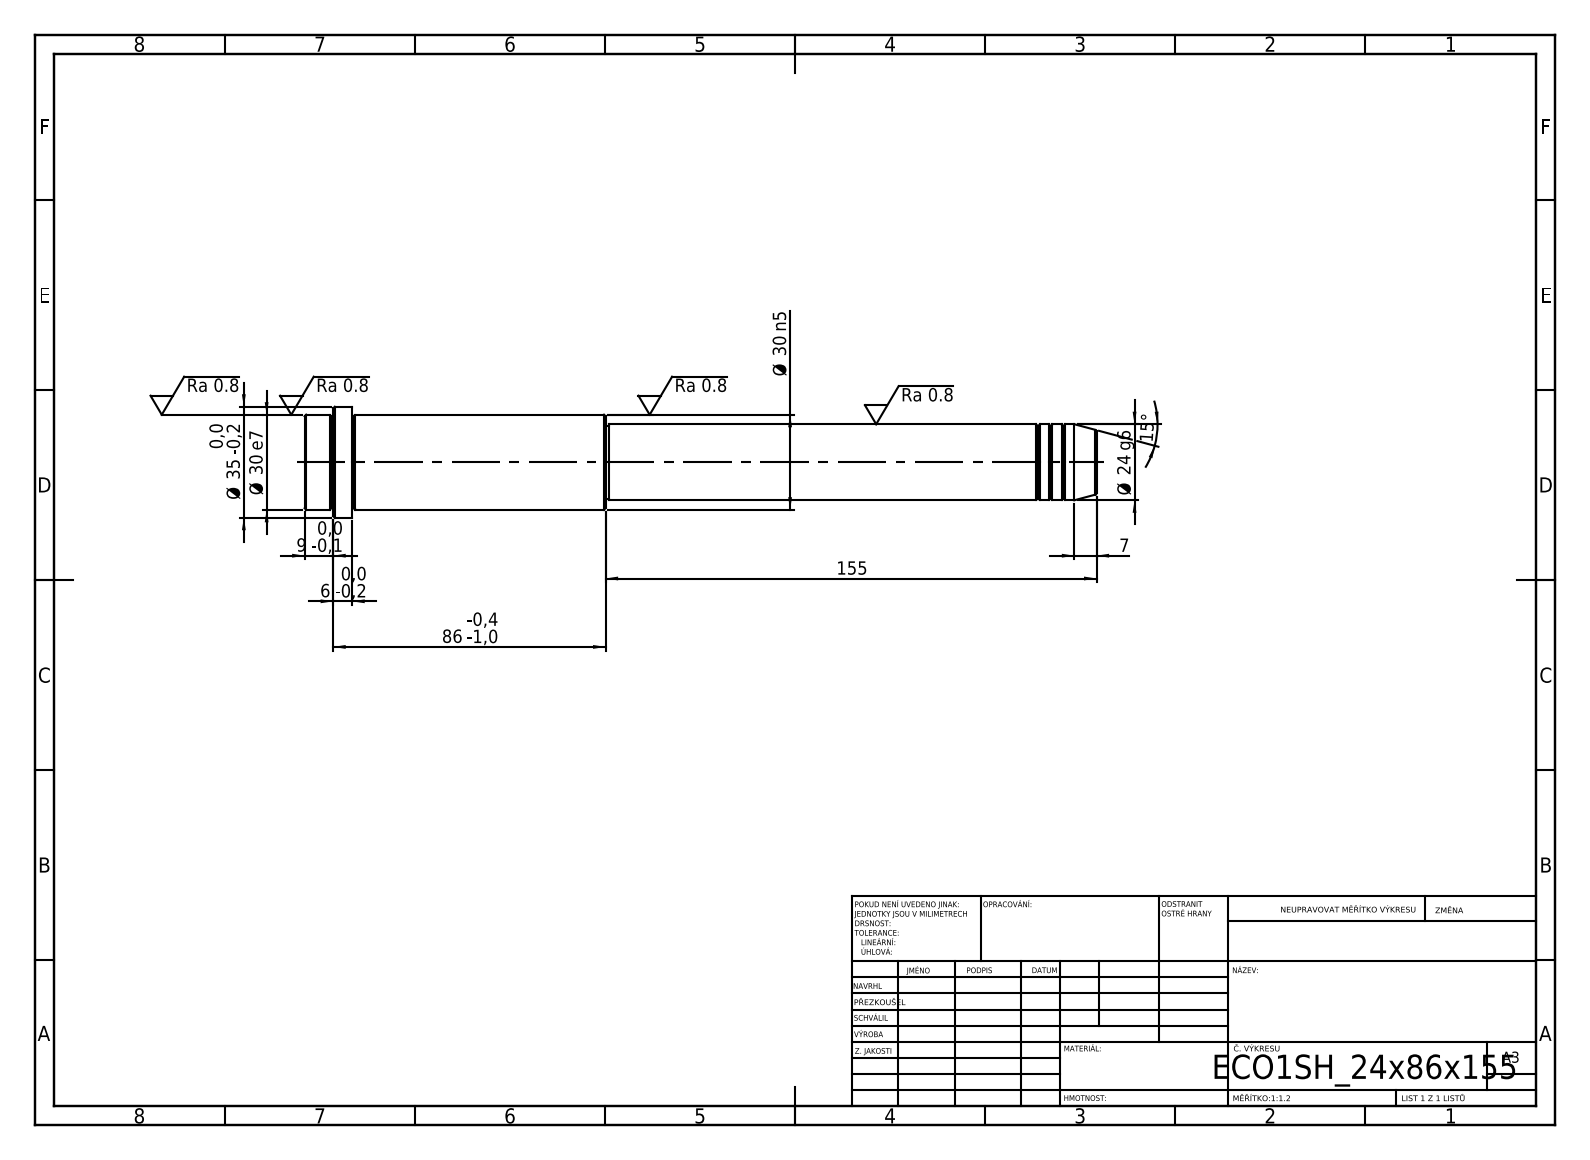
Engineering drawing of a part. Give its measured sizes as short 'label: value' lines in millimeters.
written by: SolidWorks 2019 (CONFIG_CONTROL_DESIGN)
unit: mm
bodies: 1 solid, 52 faces (6 planar, 16 cylindrical, 30 other)
size: 250 × 35 × 35
volume: 138 098 mm³; area: 22 700 mm²
bosses: 1× ⌀35, 1× ⌀30, 1× ⌀24, 1× ⌀23
face distances: 250, 235, 15, 155, 80, 95, 241, 86, 6, 9
